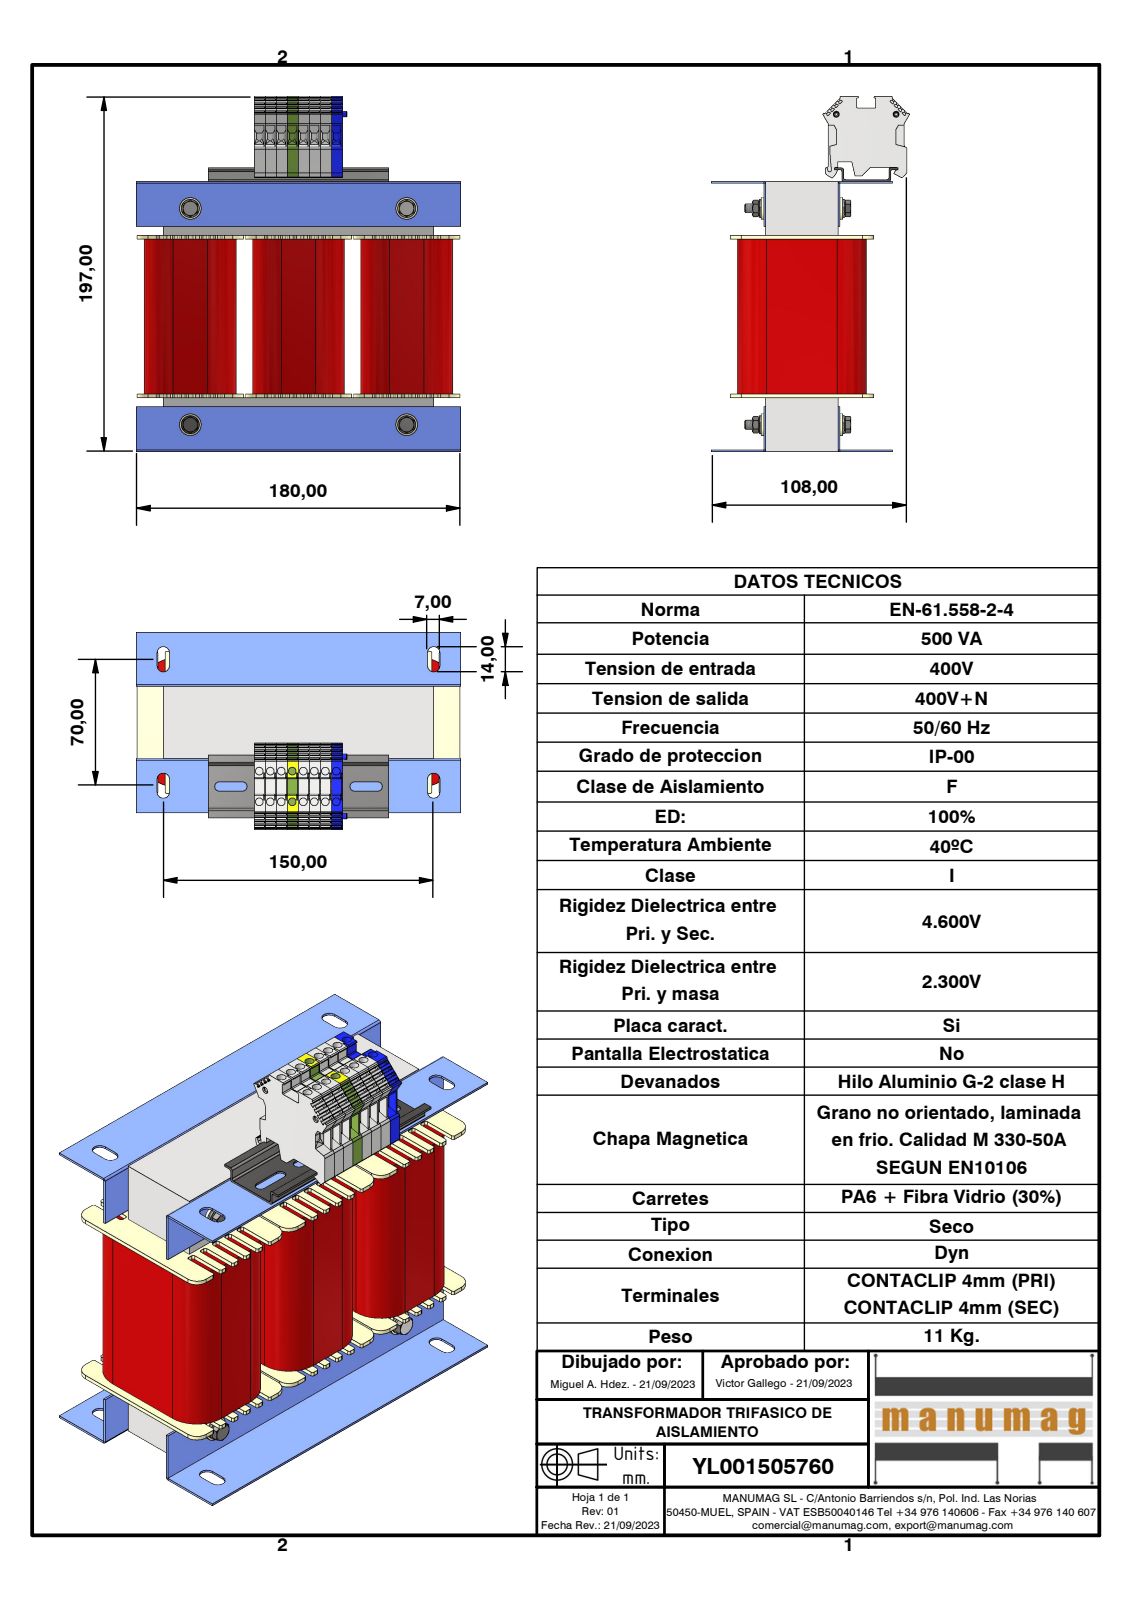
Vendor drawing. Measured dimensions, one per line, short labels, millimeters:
name: YL001505760; 3UI90 150 x 150 - 40 (Rc30); UI 90_40; RC30 NT030 (+8 more)
written by: Autodesk Inventor 2023 (AUTOMOTIVE_DESIGN)
unit: mm
bodies: 41 solids, 3082 faces (2178 planar, 736 cylindrical, 168 other)
size: 197.25 × 180 × 109.47
volume: 1 392 000 mm³; area: 347 462 mm²
holes: 16× ⌀4.3, 4× ⌀4.13, 4× ⌀5, 4× ⌀5.3, 4× ⌀6, 4× ⌀10.5, 2× ⌀2.4, 2× ⌀2.5, 2× ⌀2.75, 2× ⌀2.95
bosses: 4× ⌀12, 4× ⌀10, 4× ⌀6.7, 4× ⌀5.9, 4× ⌀4.57
rounds: 132× R1, 16× R0.25, 12× R6, 12× R16, 8× R2.6, 8× R3.5, 5× R0.3, 5× R0.5
face distances: 30, 1, 60, 120, 40, 90, 150, 119, 29, 10.5
hole spacings: 6.1, 18.06, 12.2, 20.92, 18.3, 24.98, 17, 24.4
